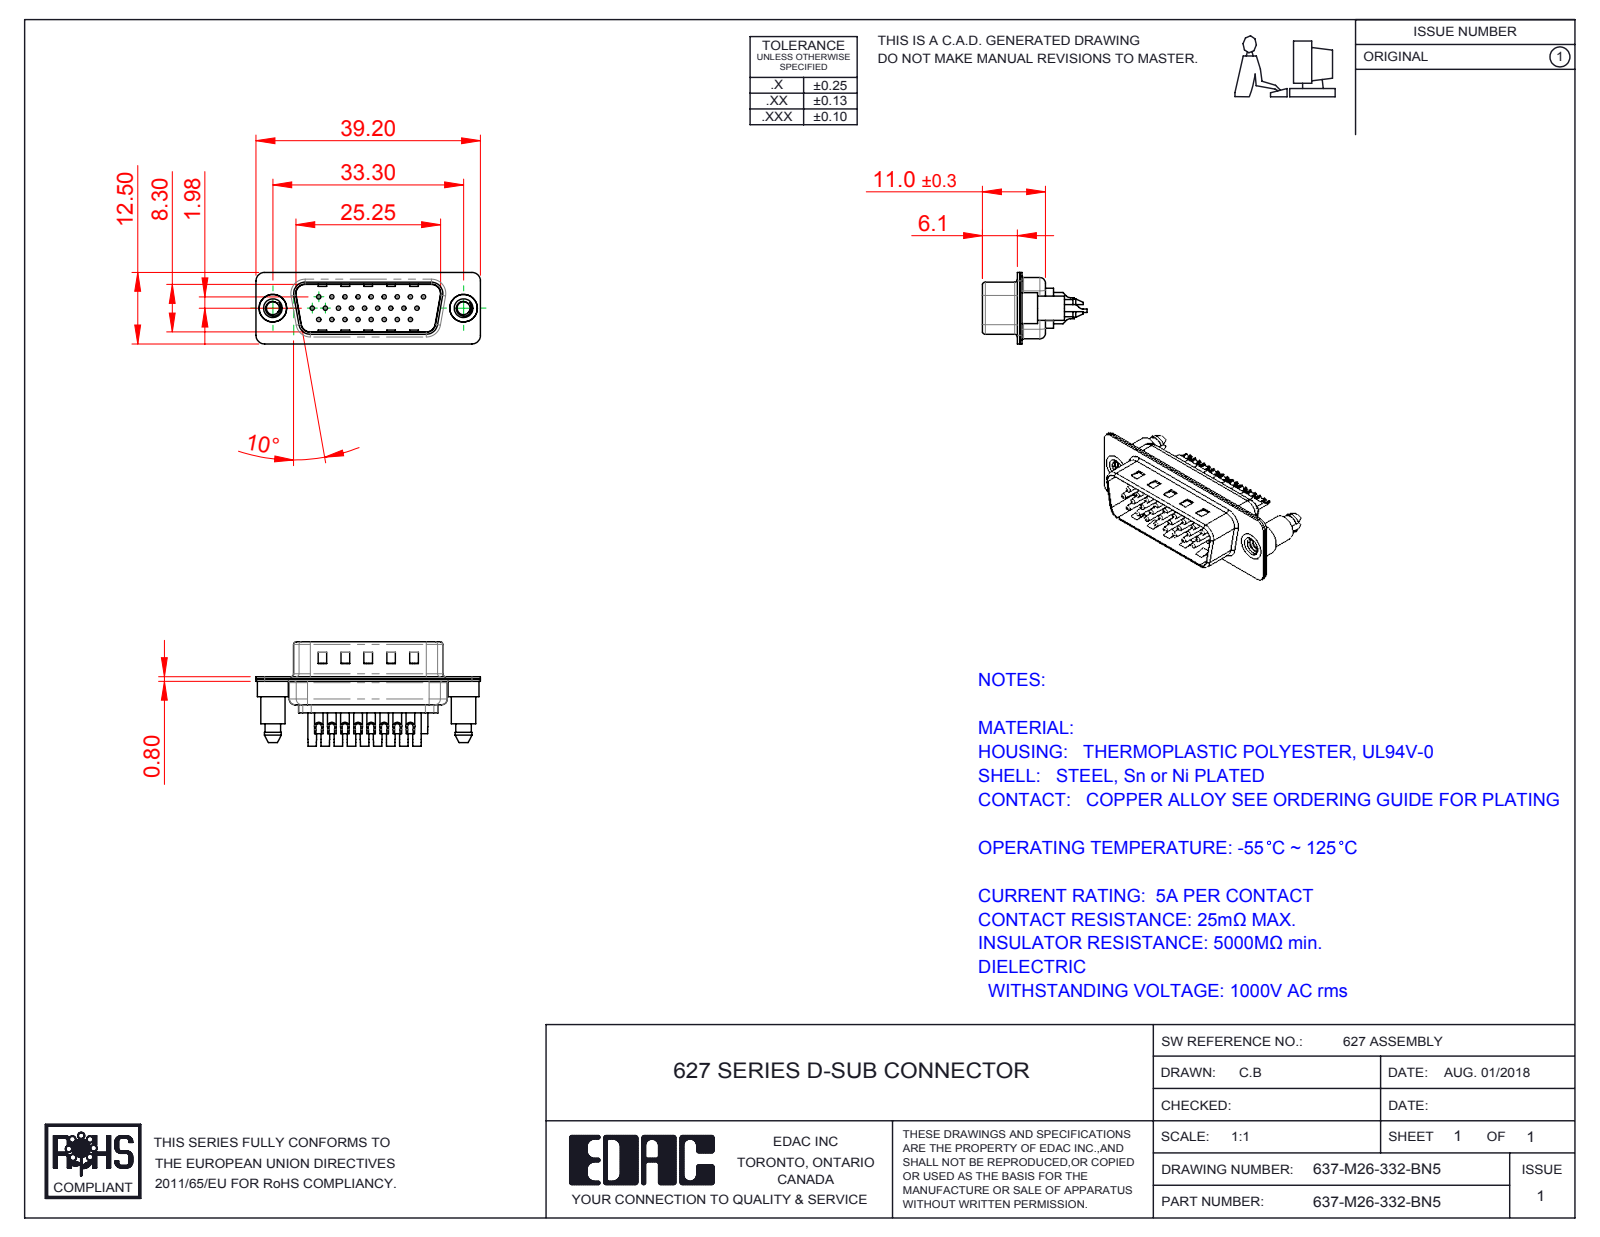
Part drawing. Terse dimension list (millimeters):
name: 637M 4-40 Threaded Boardlock; 637M Contact Row 1_32; 637M Housing_26 Contacts; 637M Contact Row 3_32 (+4 more)
written by: SolidWorks 2016 (CONFIG_CONTROL_DESIGN)
unit: mm
bodies: 31 solids, 1352 faces (389 planar, 581 cylindrical, 382 other)
size: 39.2 × 18.25 × 12.5
volume: 2 129 mm³; area: 6 406 mm²
holes: 26× ⌀0.75, 26× ⌀1, 26× ⌀1.6, 26× ⌀2, 2× ⌀2.26, 2× ⌀4, 2× ⌀4.8
bosses: 26× ⌀1.5, 2× ⌀5.4, 2× ⌀4.9, 2× ⌀4.25
rounds: 18× R1.5, 12× R2, 10× R1.6, 8× R0.5, 7× R1, 4× R0.25, 4× R0.6, 4× R0.65
face distances: 0.4, 0.8, 9.5, 9.1, 8.7, 9.9, 0.75, 0.35, 1.2, 1.9
hole spacings: 3.96, 2.28, 4.57, 6.05, 2.29, 8.24, 6.86, 10.48
